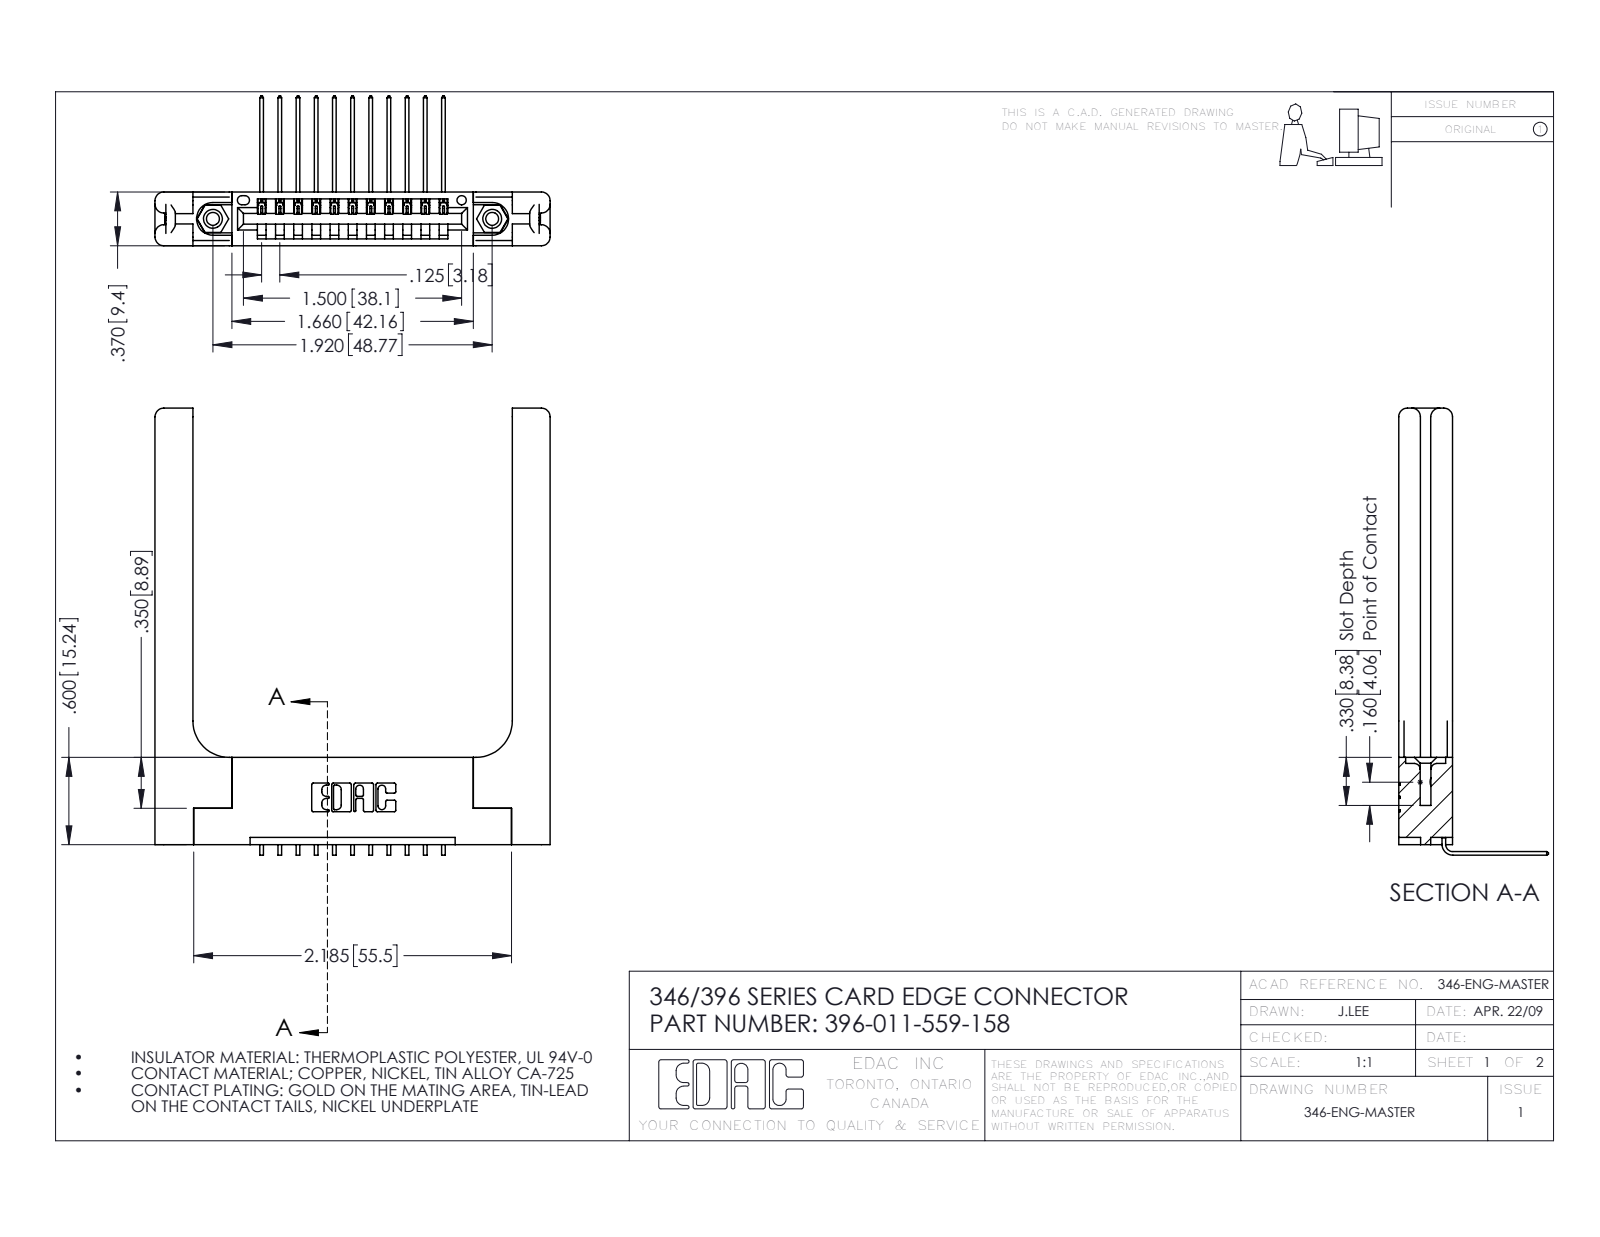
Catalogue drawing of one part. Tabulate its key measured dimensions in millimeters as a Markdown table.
| quantity | value |
| --- | --- |
| part name | 396-011-559-158; 345-250-001_345-250-001-102; 346-220-058_345-220-058; 346 Part_Flush Mounting Lugs - 0.156 Dia-TH (+1 more) |
| STEP written by | SolidWorks 2016 (CONFIG_CONTROL_DESIGN) |
| units | millimeters |
| bodies | 16 solids, 1038 faces (686 planar, 292 cylindrical, 60 other) |
| overall size | 78.1 × 69 × 26.2 |
| volume | 13 900 mm³ |
| surface area | 13 080 mm² |
| round holes (diameter × count) | 2.3 × 2, 3.2 × 2, 4 × 2, 1.6 × 1 |
| round bosses / shafts (diameter × count) | 3.9 × 2 |
| partial cylindrical surfaces (radius × count) | 0.2 × 22, 0.3 × 22, 1.5 × 16, 0.2 × 6, 0.8 × 6, 0.7 × 3, 0.8 × 2, 0.8 × 2 |
| main face-to-face distances | 9.4, 3.8, 1.8, 3.8, 5.6, 8.2, 1.2, 6.4, 2.6, 4.4 |
| hole center spacings | 6.2, 43.6, 48.8 |
